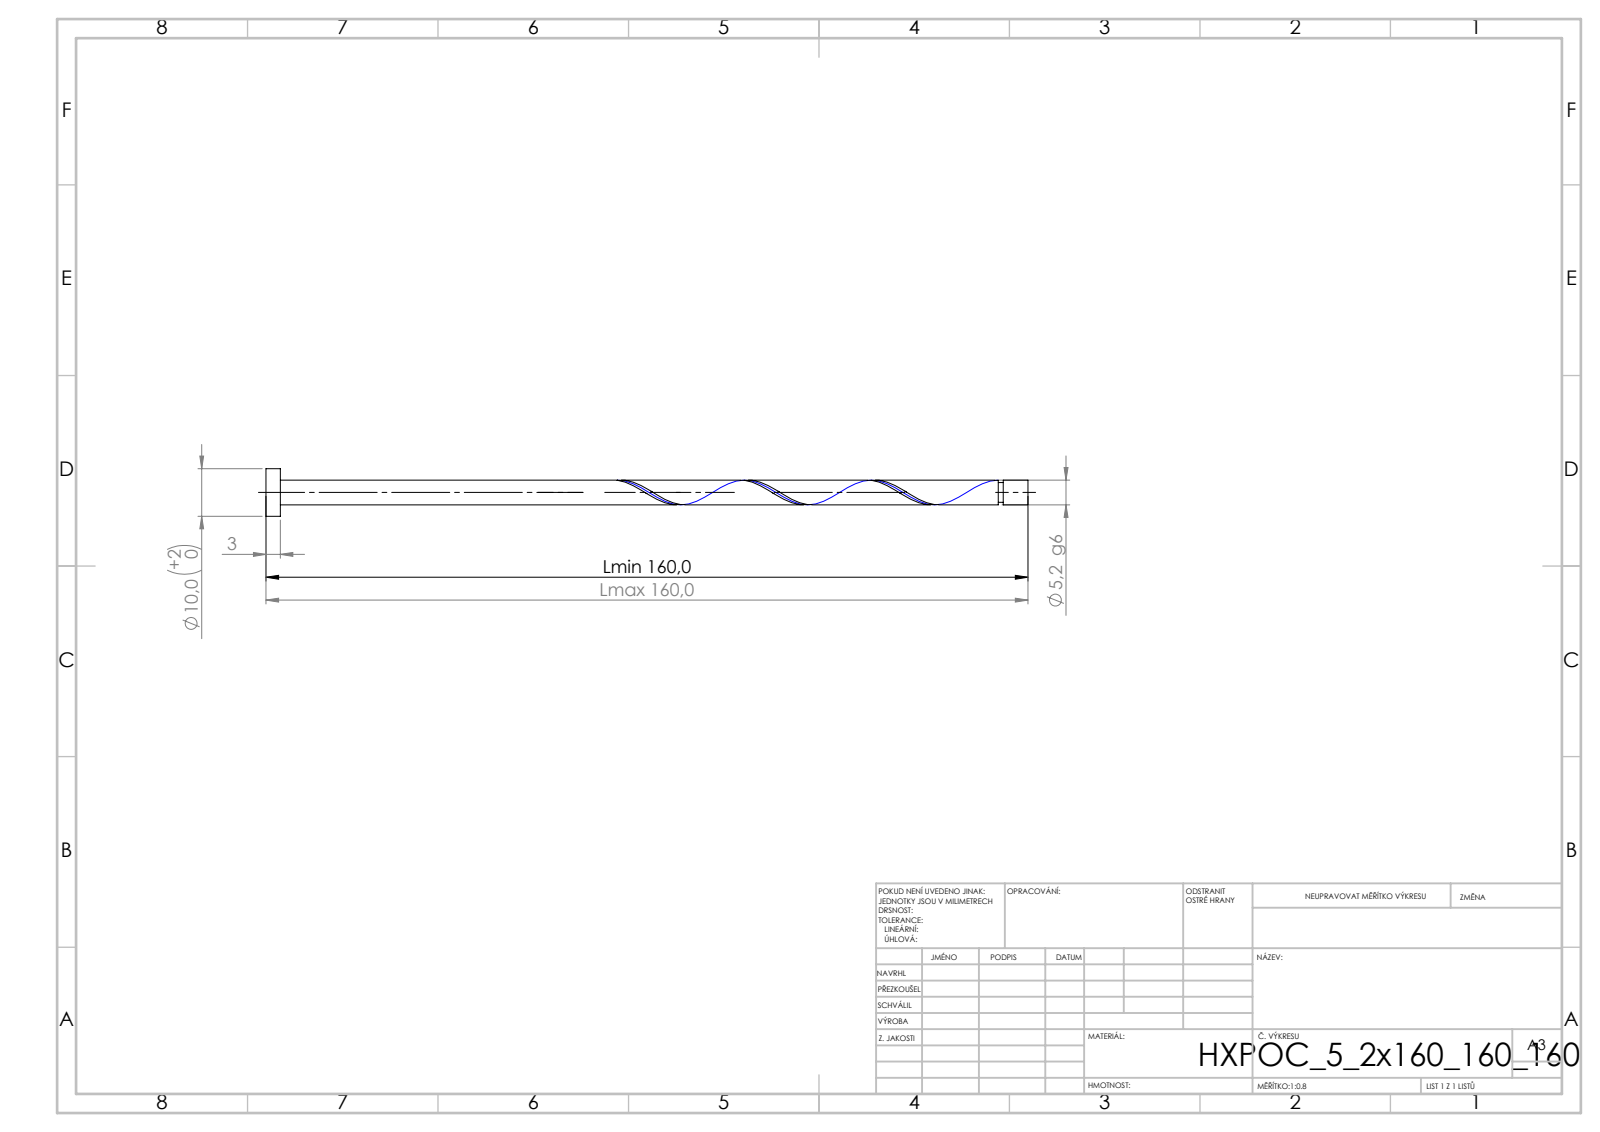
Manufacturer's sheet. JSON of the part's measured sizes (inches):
{"step_written_by": "SolidWorks 2019 (CONFIG_CONTROL_DESIGN)", "units": "inches", "bodies": {"solids": 1, "faces": 21, "planar": 6, "cylindrical": 14, "other": 1}, "overall_size": [6.299, 0.394, 0.394], "volume_in3": 0.215, "surface_area_in2": 4.459, "round_bosses_or_shafts": [[0.394, 1], [0.205, 1], [0.164, 1]], "face_to_face_distances": [0.118, 6.299, 6.181, 6.095, 5.977, 0.204, 6.054, 5.936, 0.041, 0.245]}
